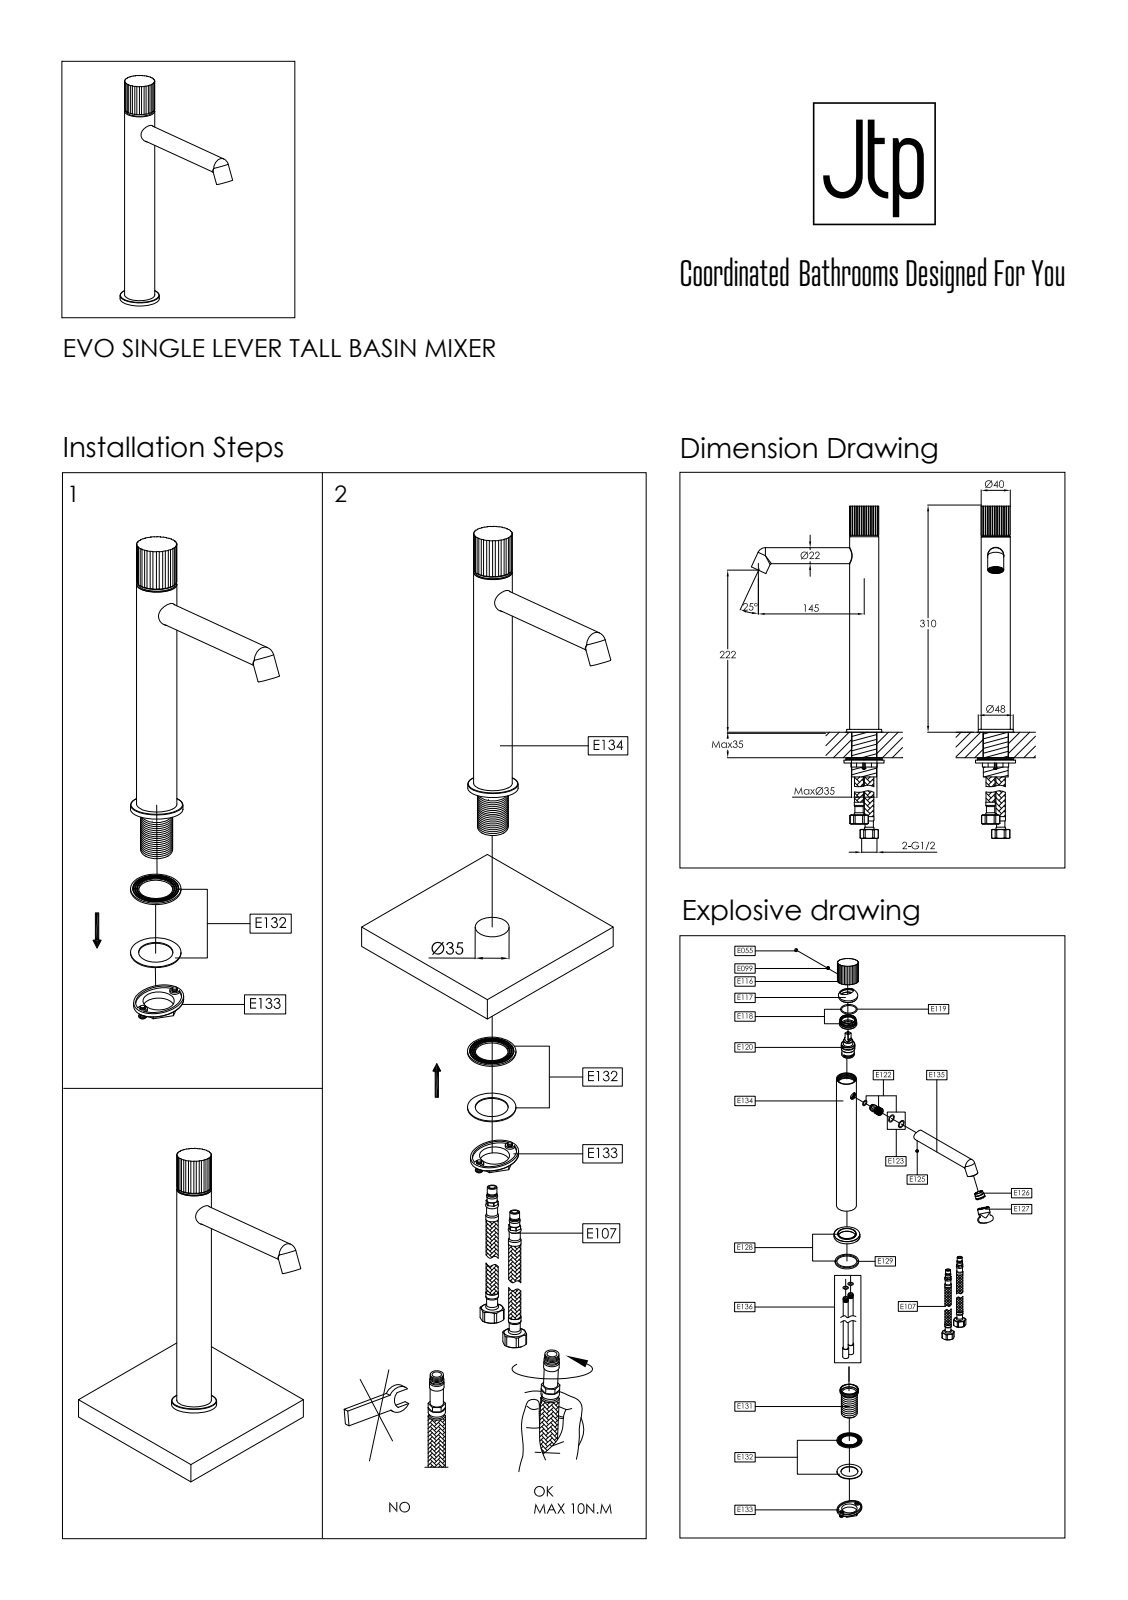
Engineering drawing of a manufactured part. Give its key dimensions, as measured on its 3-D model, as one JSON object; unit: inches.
{"part_name": "615-0301_X2_4E3B4F537BA1_X-3141; 615-0301_X2_4E3B4F537BA1_X-3140; CT25UF001_X2_960082AF_X0__ID106; X2_516D89D2538B5E3D_X0__ID102 (+8 more)", "step_written_by": "CREO PARAMETRIC BY PTC INC, 2019224 (CONFIG_CONTROL_DESIGN)", "units": "inches", "bodies": {"solids": 19, "faces": 1130, "planar": 423, "cylindrical": 446, "other": 261}, "overall_size": [12.319, 7.122, 2.047], "volume_in3": 9.512, "surface_area_in2": 202, "round_holes": [[0.197, 4], [0.433, 3], [0.138, 2], [0.169, 2], [0.354, 2], [0.13, 1], [0.205, 1], [0.256, 1], [0.394, 1], [0.512, 1], [0.531, 1], [0.551, 1]], "round_bosses_or_shafts": [[0.866, 2], [0.669, 2], [0.197, 2], [0.118, 2], [2.047, 1], [1.587, 1], [1.575, 1], [1.472, 1]], "partial_cylinders_radius": [[0.004, 150], [0.008, 2], [0.039, 2], [0.079, 2], [0.031, 1], [0.094, 1], [0.098, 1], [0.11, 1]], "face_to_face_distances": [0.059, 0.031, 0.197, 12.161, 12.102, 0.138, 9.035, 8.976, 3.126, 0.079], "hole_center_spacings": [0.02, 0.181, 0.198, 0.201, 0.244, 0.257, 0.276, 0.371]}
